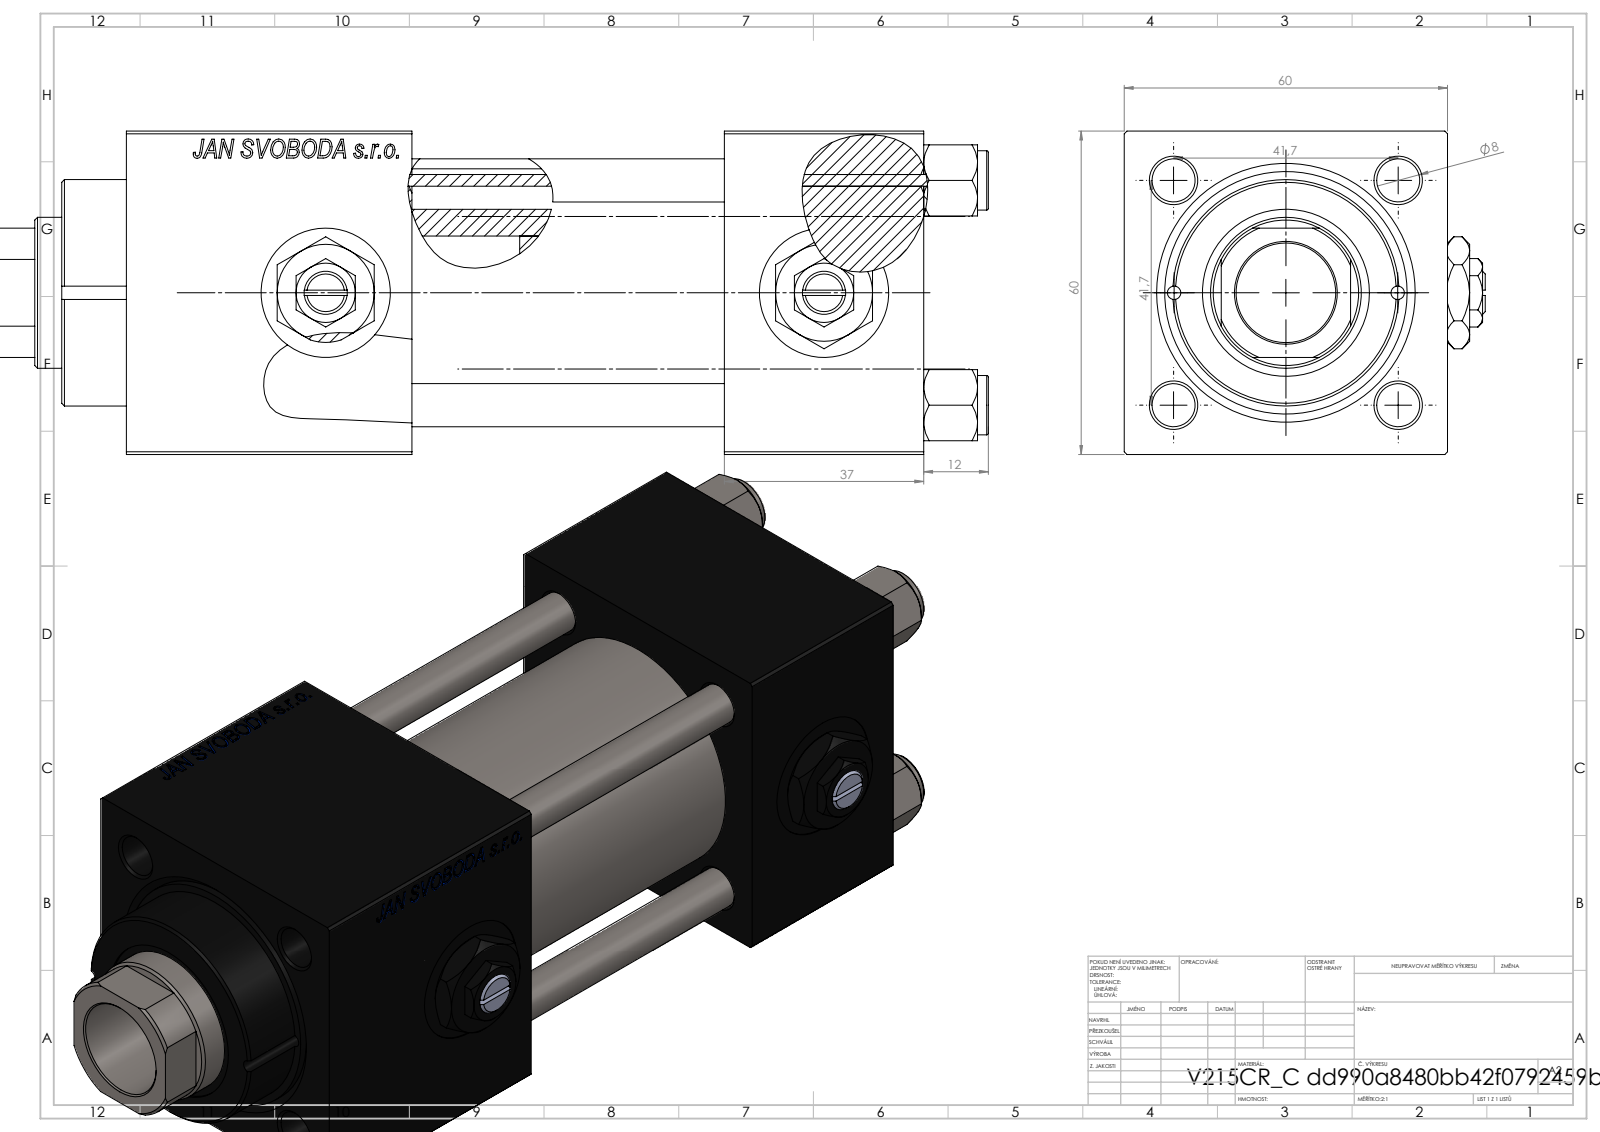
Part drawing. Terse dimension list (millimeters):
name: V215_VC_A; V215CR_VCP_C; V215CR_C_Body; NUT_M5_C (+2 more)
written by: SolidWorks 2019 (CONFIG_CONTROL_DESIGN)
unit: mm
bodies: 13 solids, 1256 faces (576 planar, 102 cylindrical, 578 other)
size: 185 × 67 × 60
volume: 420 815 mm³; area: 114 475 mm²
holes: 4× ⌀8, 2× ⌀2.5, 2× ⌀7, 2× ⌀16.66, 2× ⌀24, 1× ⌀18.5, 1× ⌀28, 1× ⌀31, 1× ⌀40, 1× ⌀45
bosses: 4× ⌀11, 1× ⌀46, 1× ⌀42
rounds: 1× R13.5
face distances: 60, 37, 58, 95, 53, 119.3, 82.3, 24.3, 148, 111
hole spacings: 20.85, 29.49, 41.7, 46.53, 20.75, 58.97, 41.5, 92.5
